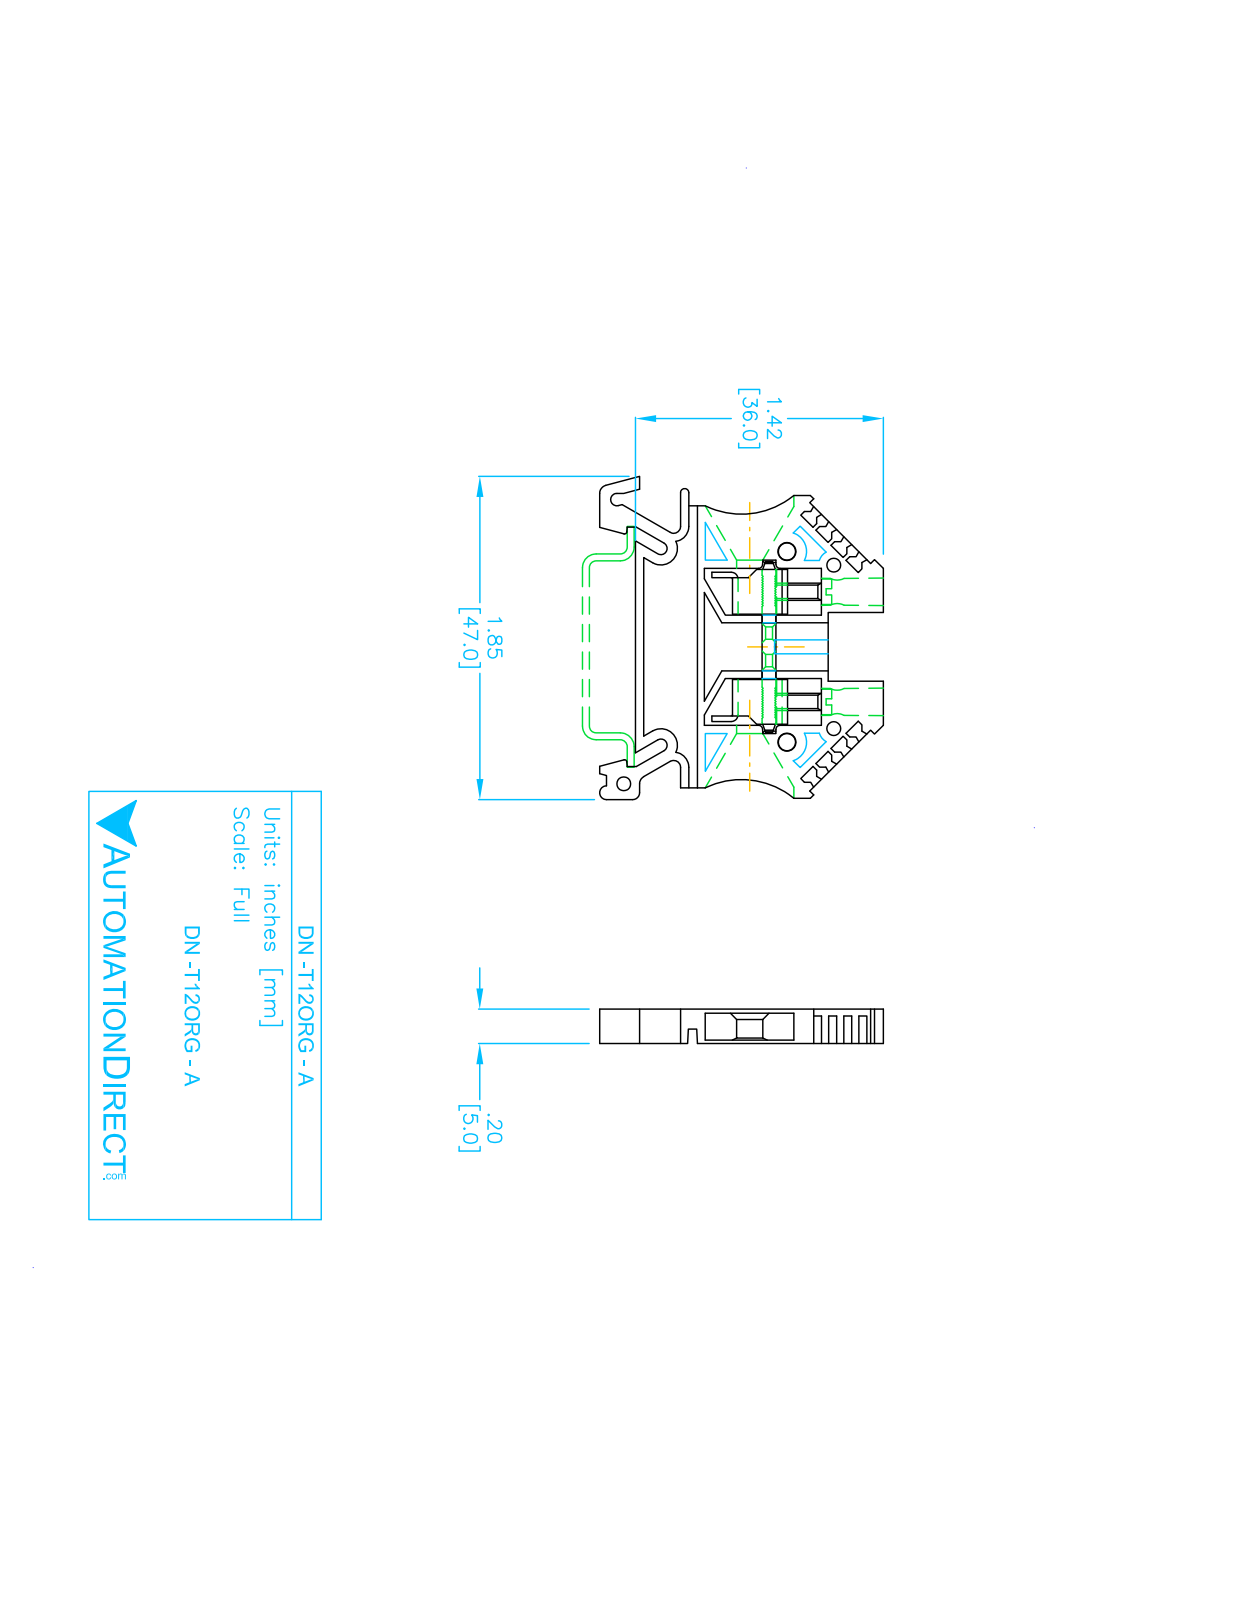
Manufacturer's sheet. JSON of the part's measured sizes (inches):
{"part_name": "DN-T12ORG-A", "step_written_by": "SolidWorks 2017 (AUTOMOTIVE_DESIGN)", "units": "inches", "bodies": {"solids": 1, "faces": 169, "planar": 134, "cylindrical": 35, "other": 0}, "overall_size": [1.85, 1.622, 0.197], "volume_in3": 0.306, "surface_area_in2": 7.131, "round_holes": [[0.164, 2], [0.079, 1]], "partial_cylinders_radius": [[0.039, 4], [0.035, 3], [0.012, 2], [0.047, 2], [0.087, 2], [0.094, 2], [0.472, 2], [0.024, 1]], "face_to_face_distances": [0.189, 0.197, 0.087, 0.02, 0.106, 0.094, 0.114, 0.083, 0.102, 0.354], "hole_center_spacings": [0.589]}
